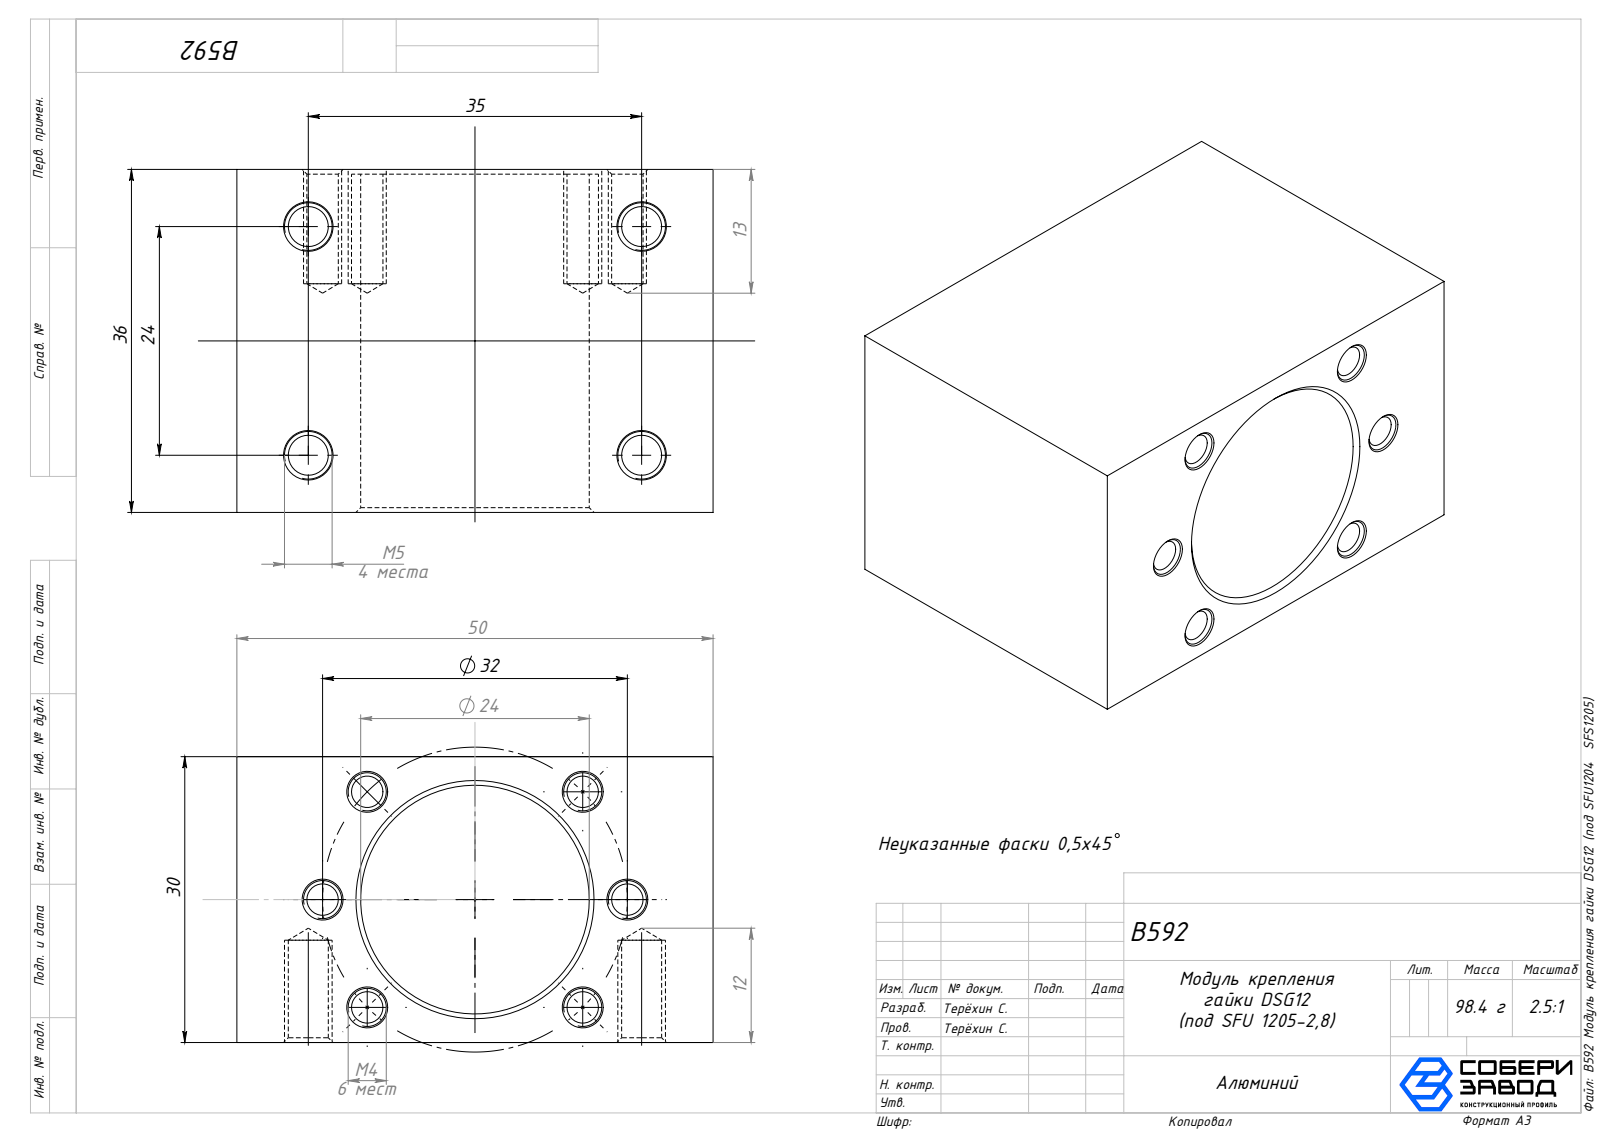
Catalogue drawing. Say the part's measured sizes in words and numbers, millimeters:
The part is named "B592 Модуль крепления гайки DSG12 (под SFU1204 SFS1205)_DSG12H; B592 Модуль крепления гайки DSG12 (под SFU1204 SFS1205)". Its 3-D file was written by "SolidWorks 2025 (CONFIG_CONTROL_DESIGN)". It is 1 solid with 72 faces: 6 planar, 22 cylindrical and 44 other. Overall it measures 50 by 36 by 30 millimeters. Its volume is 36 428 cubic millimeters and its surface area 11 827 square millimeters. Round holes: 6 of diameter 3.3, 4 of diameter 4.2, 1 of diameter 24. The main face-to-face distances are 30, 50, 36. The hole center spacings are 12.24, 15.99, 22.62, 29.56, 16, 24, 31.99, 35.
